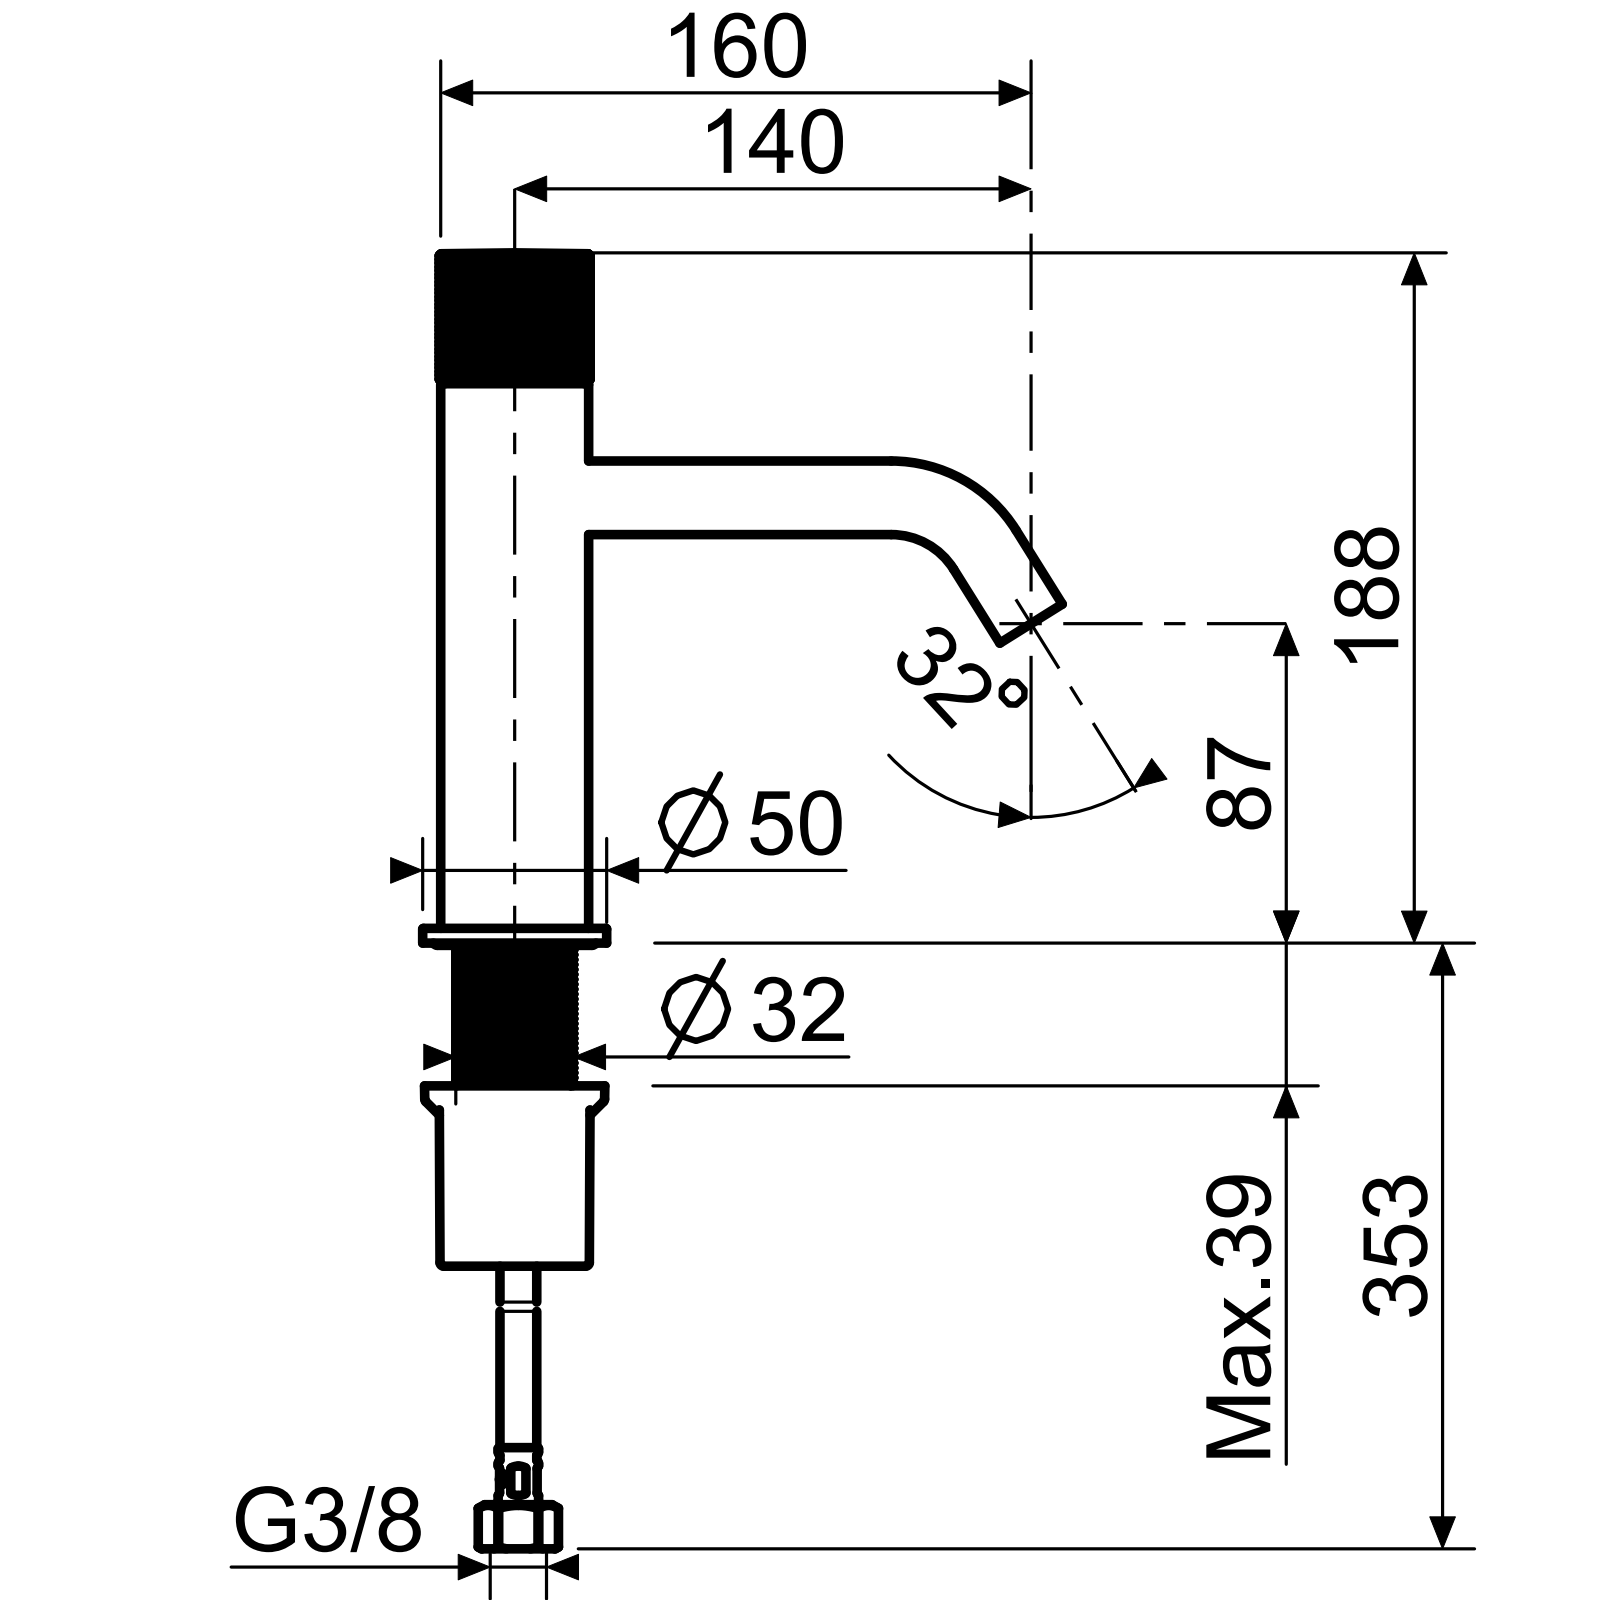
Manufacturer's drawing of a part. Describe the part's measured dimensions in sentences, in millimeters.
The part is named "ALOG201C001; ALOG007C001; ALOG201W001; SCCMAC0007 (+4 more)". Its 3-D file was written by "CREO PARAMETRIC BY PTC INC, 2022164 (CONFIG_CONTROL_DESIGN)". It is 7 solids with 6552 faces: 2903 planar, 1279 cylindrical and 2370 other. Overall it measures 187.56 by 173.8 by 50 millimeters. Its volume is 93 773 cubic millimeters and its surface area 79 260 square millimeters. Round holes: 1 of diameter 4.2, 1 of diameter 5.1, 1 of diameter 9, 1 of diameter 10.3, 1 of diameter 11, 1 of diameter 12.15, 1 of diameter 14.55, 1 of diameter 15, 1 of diameter 15.55, 1 of diameter 16.75, 1 of diameter 26.5, 1 of diameter 30. Round bosses or shafts: 2 of diameter 20, 1 of diameter 50, 1 of diameter 40.2, 1 of diameter 40, 1 of diameter 37.8, 1 of diameter 32, 1 of diameter 18, 1 of diameter 16.5. Partial cylindrical surfaces (rounded edges, fillets, slot ends): 2 of radius 1, 2 of radius 2.5, 2 of radius 3, 1 of radius 1.5, 1 of radius 4, 1 of radius 6.22, 1 of radius 6.5, 1 of radius 7.54. The main face-to-face distances are 2, 4, 184.8, 180.8, 28.42, 182.8, 28.44, 149.95, 147.95, 145.95.
